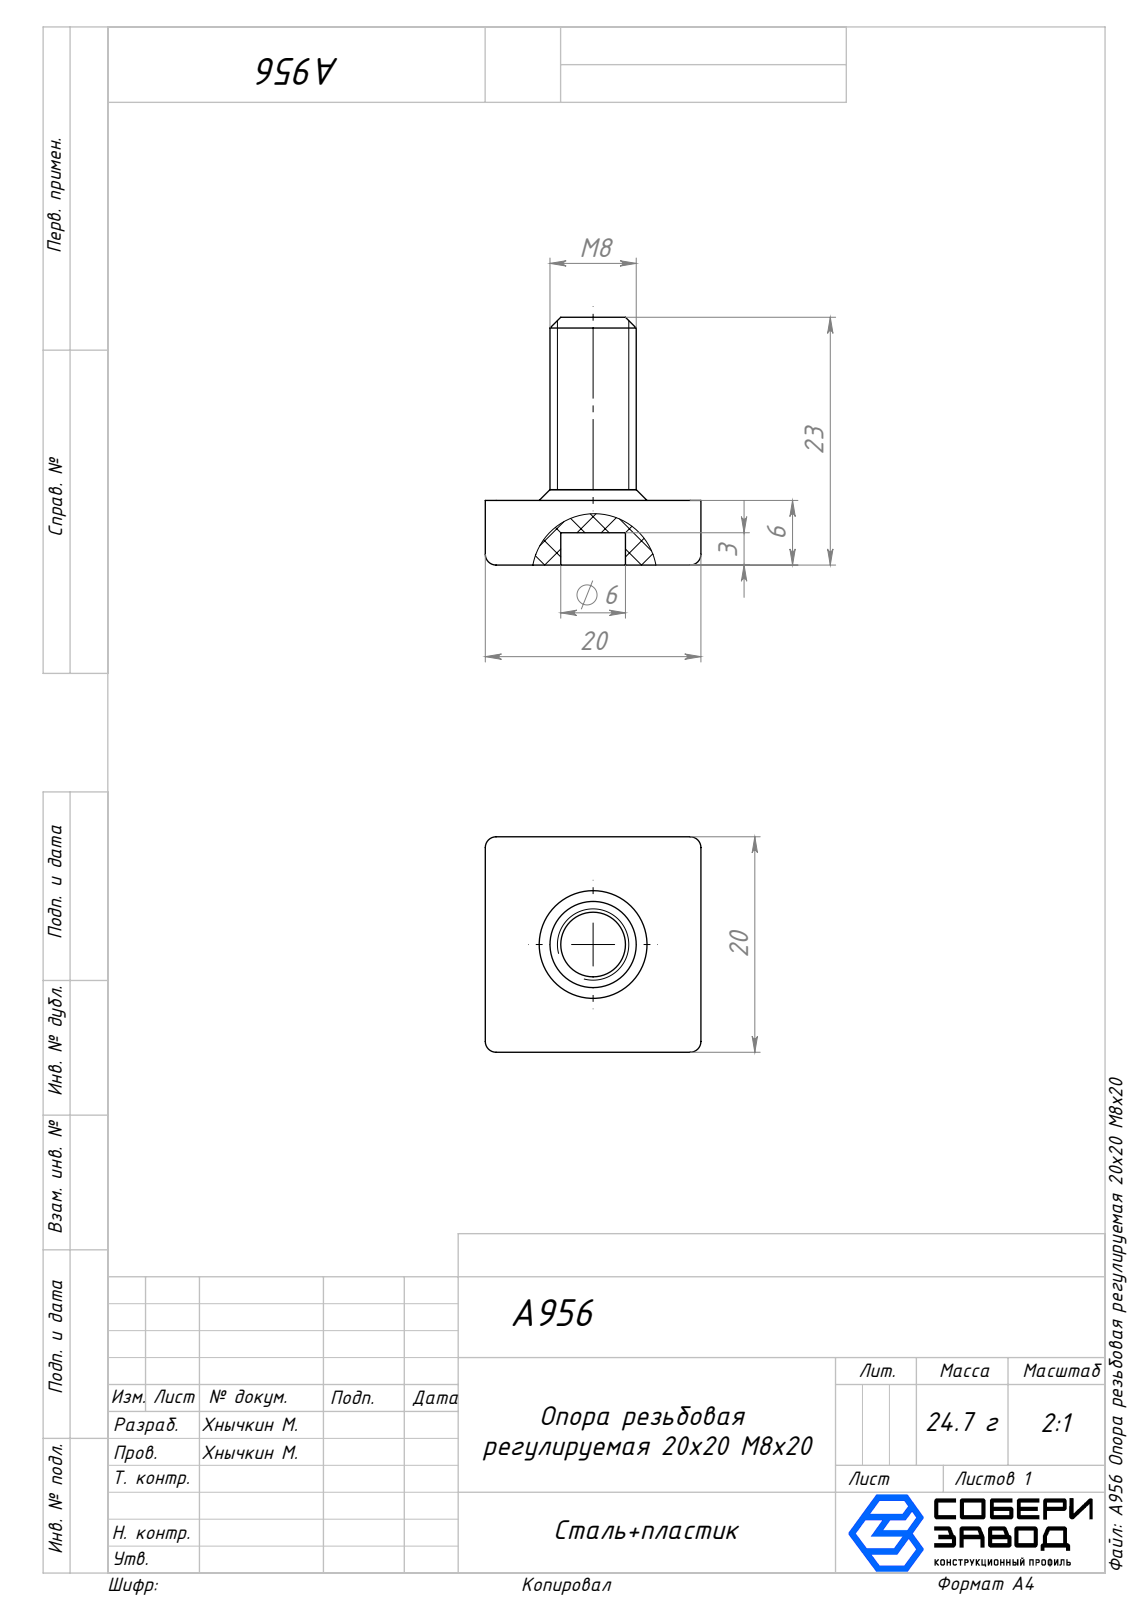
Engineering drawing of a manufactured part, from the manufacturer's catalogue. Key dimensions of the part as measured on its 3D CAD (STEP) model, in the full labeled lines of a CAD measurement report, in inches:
Part name (STEP PRODUCT): A956 Опора резьбовая регулируемая 20х20 М8x20
STEP written by: SolidWorks 2025 (AUTOMOTIVE_DESIGN)
Units: inches
Bodies: 1 solid, 28 faces (8 planar, 12 cylindrical, 8 other)
Overall size (bounding box): 0.906 × 0.787 × 0.787
Volume: 0.192 in³ · Surface area: 2.616 in²
Round holes (diameter × count): ⌀0.236 ×1
Round bosses / shafts (diameter × count): ⌀0.315 ×1
Partial cylindrical surfaces — rounded edges, fillets, slot ends (radius × count): R0.039 ×8
Main face-to-face distances: 0.236, 0.787, 0.118, 0.906, 0.669
